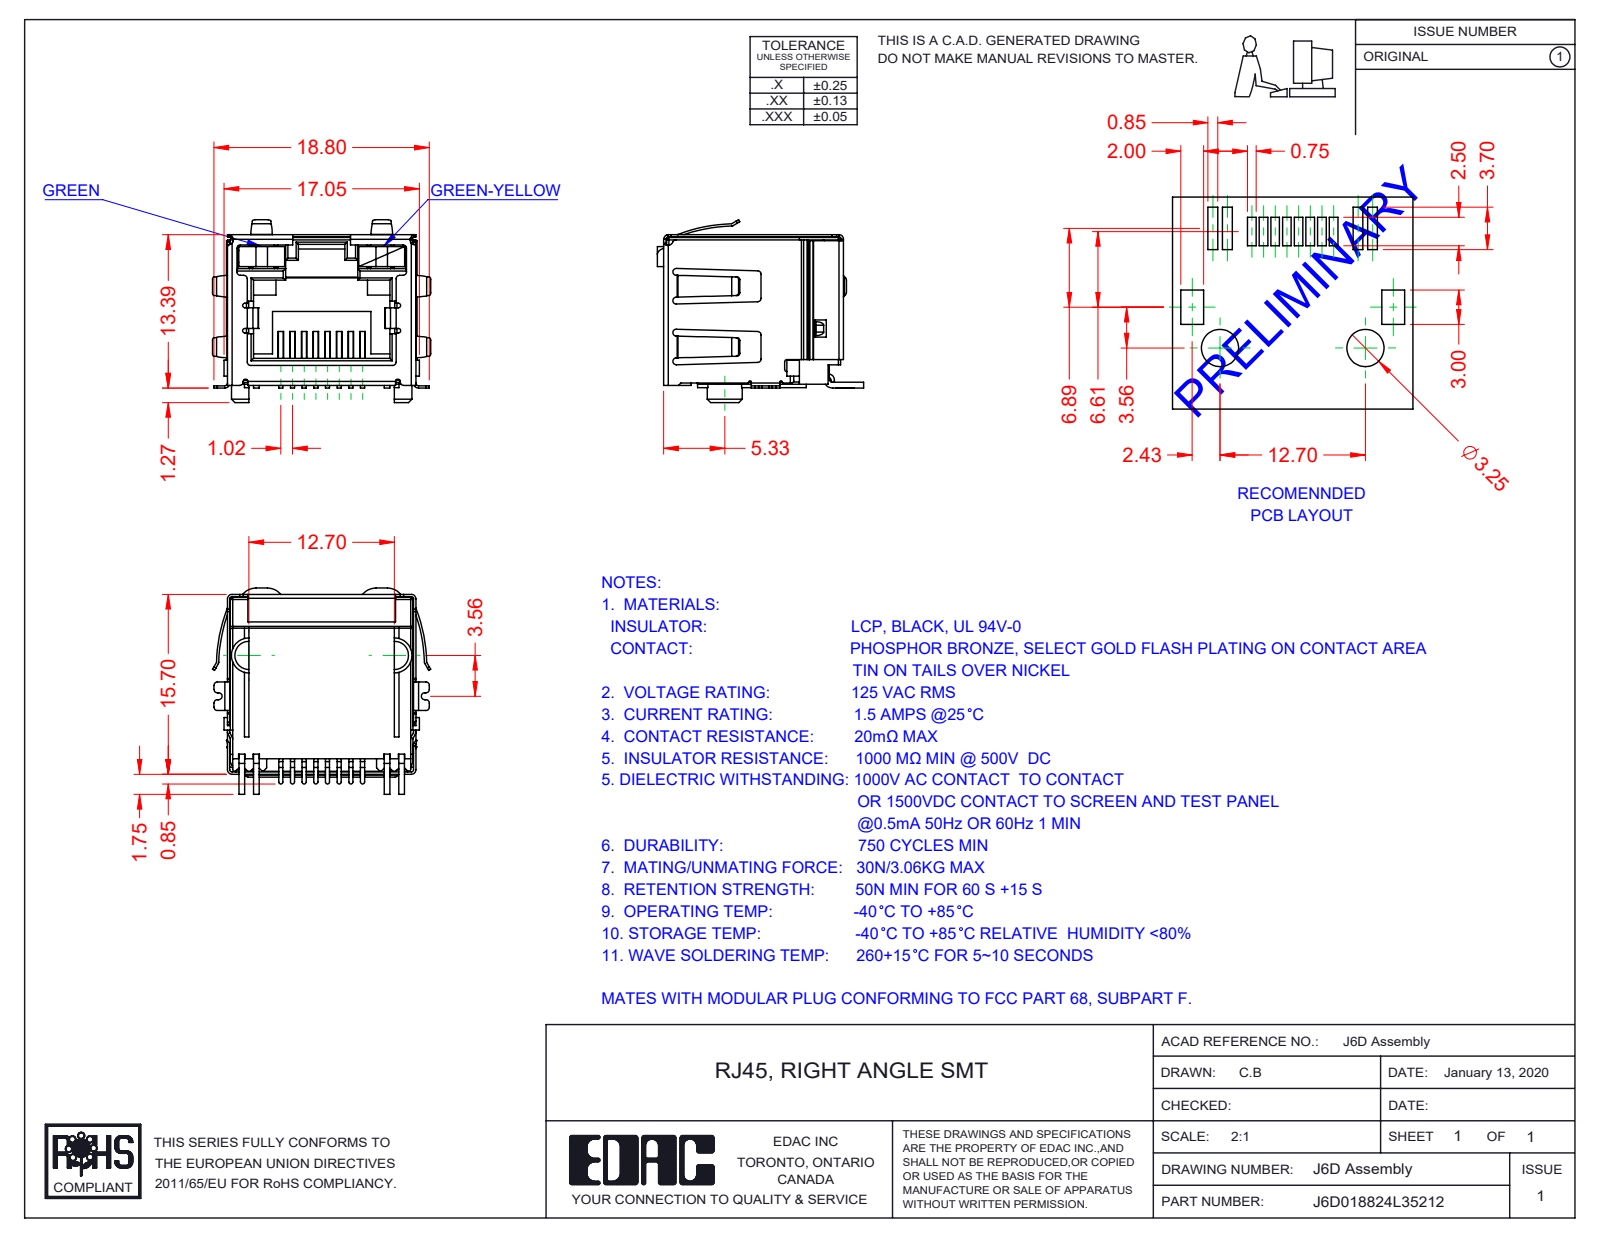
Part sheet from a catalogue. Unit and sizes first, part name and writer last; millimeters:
Units: millimetres
Overall size (bounding box): 19.06 × 18 × 15.95
Partial cylindrical surfaces — rounded edges, fillets, slot ends (radius × count): R0.3 ×55, R0.2 ×40, R0.4 ×19, R0.25 ×16, R0.1 ×12, R0.15 ×8, R0.18 ×8, R0.5 ×6
Main face-to-face distances: 16, 16.2, 16.25, 2.25, 1, 15.95, 12.8, 0.45, 13.05, 10.6
Volume: 1 790 mm³ · Surface area: 4 796 mm²
Bodies: 12 solids, 1031 faces (702 planar, 284 cylindrical, 45 other)
Part name (STEP PRODUCT): 6D LED RH_5-Green-Yellow; 6D Insulator; J6D018824L35212; 6D Shield_LED - EMI (+2 more)
STEP written by: SolidWorks 2016 (CONFIG_CONTROL_DESIGN)
